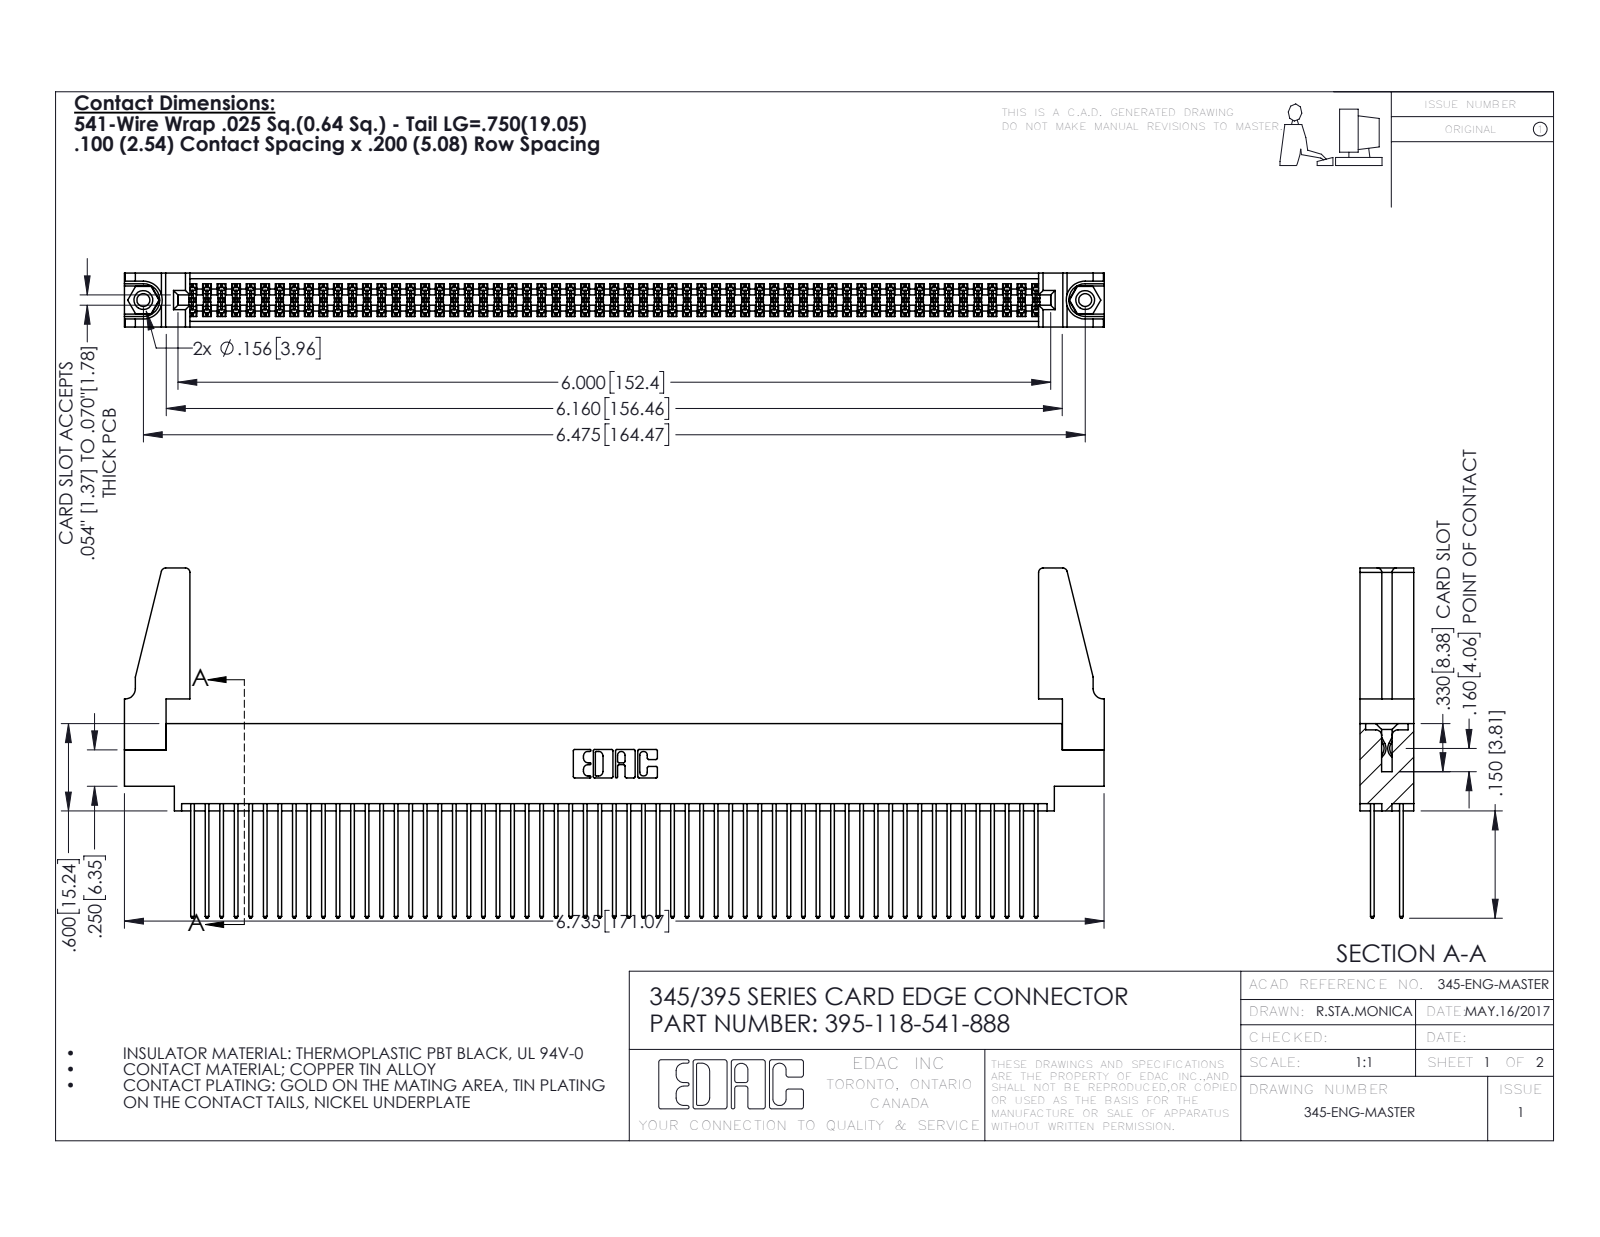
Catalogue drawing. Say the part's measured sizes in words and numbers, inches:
The part is named "395-118-541-888; 345-292-001_345-293-141; 345-250-001_345-250-001-102; 345 Part_0.170 Offset - 0.156 Dia-TH (+1 more)". Its 3-D file was written by "SolidWorks 2016 (CONFIG_CONTROL_DESIGN)". It is 123 solids with 6154 faces: 4050 planar, 2088 cylindrical and 16 other. Overall it measures 6.736 by 2.407 by 0.37 inches. Its volume is 1.257 cubic inches and its surface area 50.24 square inches. Round holes: 2 of diameter 0.089, 2 of diameter 0.125, 2 of diameter 0.156, 1 of diameter 0.064. Round bosses or shafts: 2 of diameter 0.155. Partial cylindrical surfaces (rounded edges, fillets, slot ends): 177 of radius 0.006, 118 of radius 0.01, 22 of radius 0.01, 8 of radius 0.03, 6 of radius 0.007, 6 of radius 0.031, 3 of radius 0.026, 2 of radius 0.014. The main face-to-face distances are 0.072, 0.298, 0.098, 0.272, 0.025, 0.2, 0.37, 0.225, 0.175, 0.149. The hole center spacings are 0.27, 6.239, 6.475.
